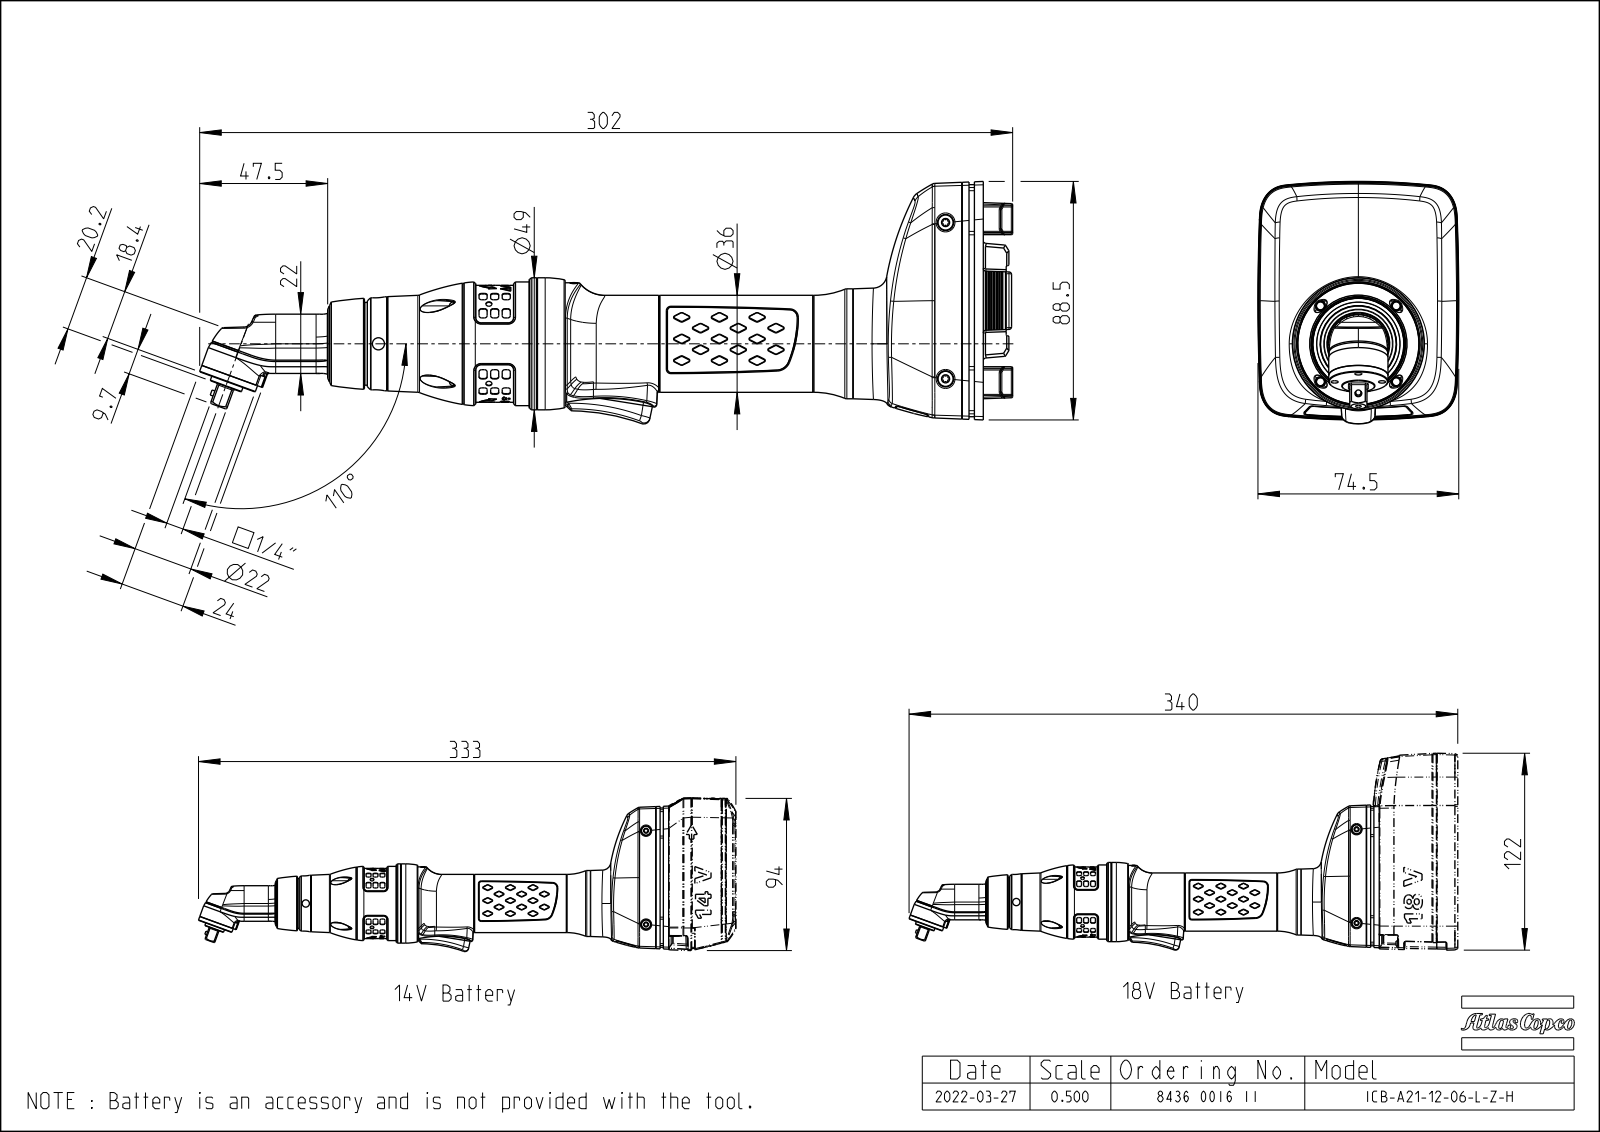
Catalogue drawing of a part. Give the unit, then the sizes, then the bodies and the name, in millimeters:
Units: millimetres
Overall size (bounding box): 301.8 × 90 × 74.5
Round holes (diameter × count): ⌀2.6 ×4, ⌀4.5 ×2, ⌀6 ×2, ⌀1 ×1, ⌀1.1 ×1, ⌀1.6 ×1, ⌀2.5 ×1, ⌀3.5 ×1, ⌀45.4 ×1
Round bosses / shafts (diameter × count): ⌀8 ×4, ⌀3.2 ×4, ⌀2.9 ×4, ⌀5.6 ×3, ⌀49 ×1, ⌀47.4 ×1, ⌀45.9 ×1, ⌀45.3 ×1
Partial cylindrical surfaces — rounded edges, fillets, slot ends (radius × count): R0.5 ×92, R1 ×54, R0.3 ×30, R0.5 ×30, R0.4 ×24, R0.7 ×24, R0.3 ×14, R2 ×12
Main face-to-face distances: 120.5, 120.5, 3, 10.5, 8.4, 131, 131, 60, 10.8, 120.2
Hole centre spacings: 8.8, 12.4, 17.6, 58, 210.9, 215.3, 230.6
Volume: 471 900 mm³ · Surface area: 66 060 mm²
Bodies: 2 solids, 2608 faces (756 planar, 649 cylindrical, 1203 other)
Part name (STEP PRODUCT): EXT_COMP_SW0014
STEP written by: CREO PARAMETRIC BY PTC INC, 2020281 (CONFIG_CONTROL_DESIGN)
